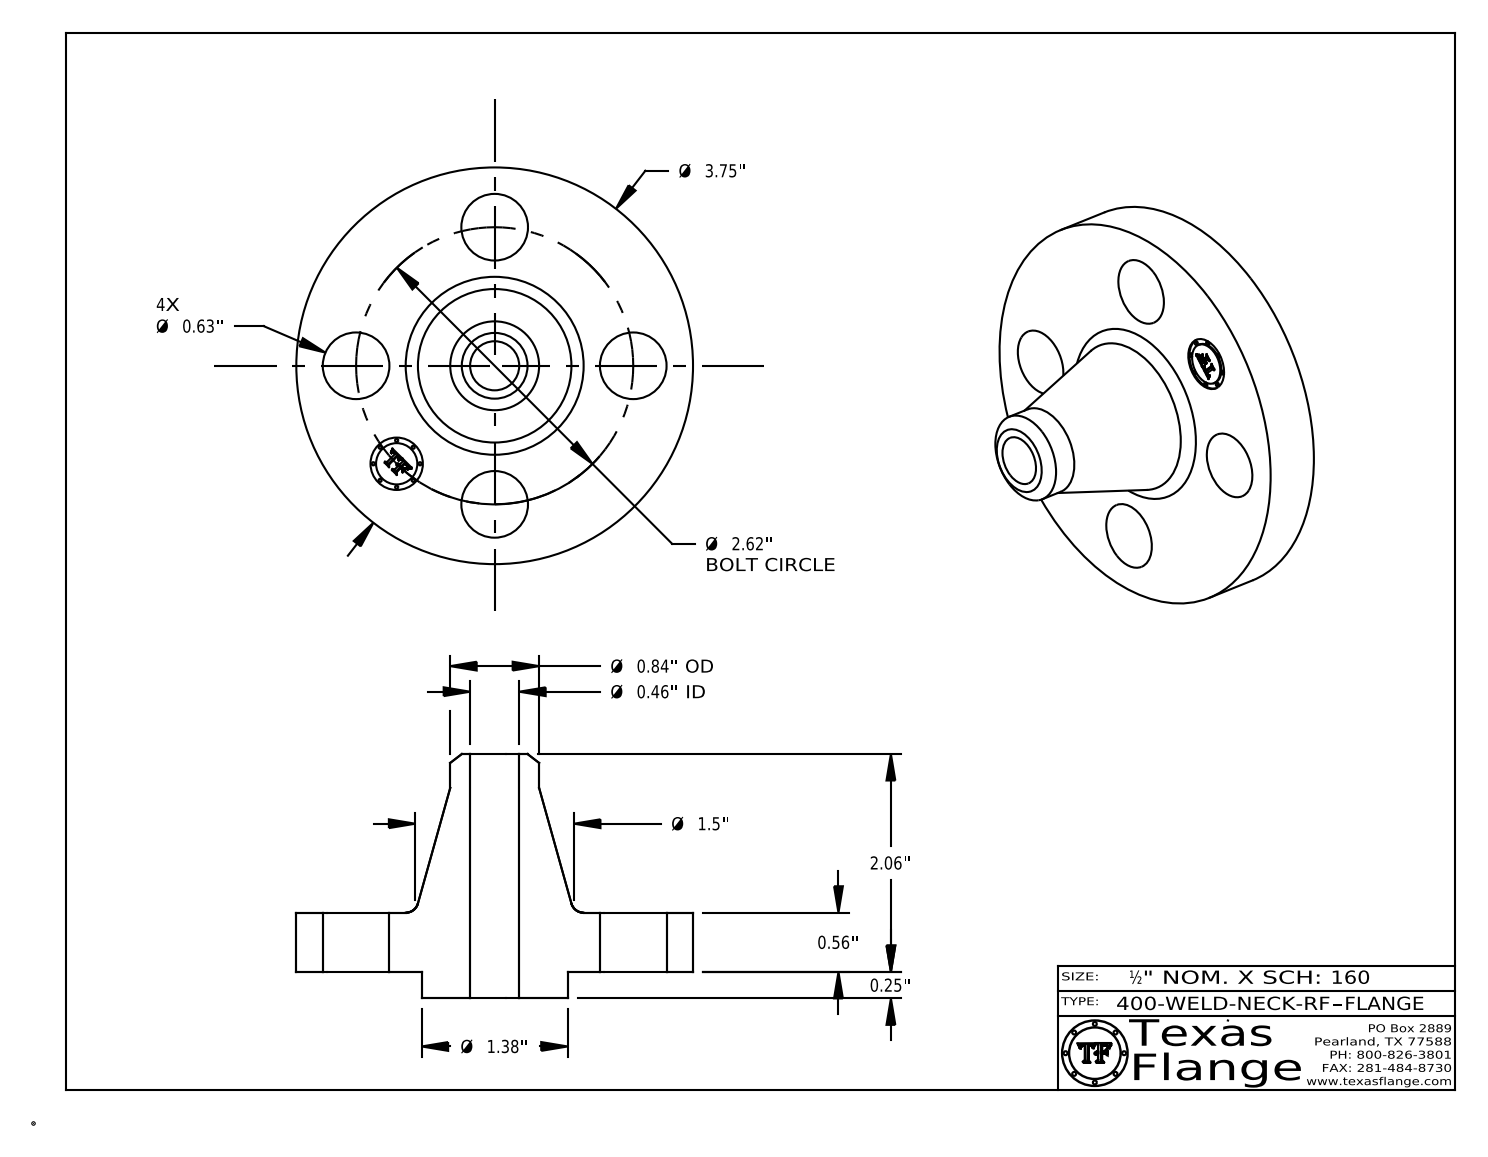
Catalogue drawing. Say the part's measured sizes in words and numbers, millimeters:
The part is named "400-WELD-NECK-RF". Its 3-D file was written by "CATIA V5 STEP AP214 (AUTOMOTIVE_DESIGN)". It is 1 solid with 411 faces: 369 planar, 36 cylindrical and 6 other. Overall it measures 95.3 by 95.3 by 58.7 millimeters. Its volume is 113 800 cubic millimeters and its surface area 24 960 square millimeters. Round holes: 4 of diameter 16, 1 of diameter 11.8, 1 of diameter 12.6. Round bosses or shafts: 8 of diameter 0.8, 1 of diameter 95.3, 1 of diameter 35.1, 1 of diameter 21.3, 1 of diameter 9.9. The main face-to-face distances are 14.2, 6.4, 20.6, 58.7, 52.3, 38.1, 20.2, 13.8, 0.4, 38.5. The hole center spacings are 33.3, 47, 25.5, 61.5, 66.5, 33.3.
